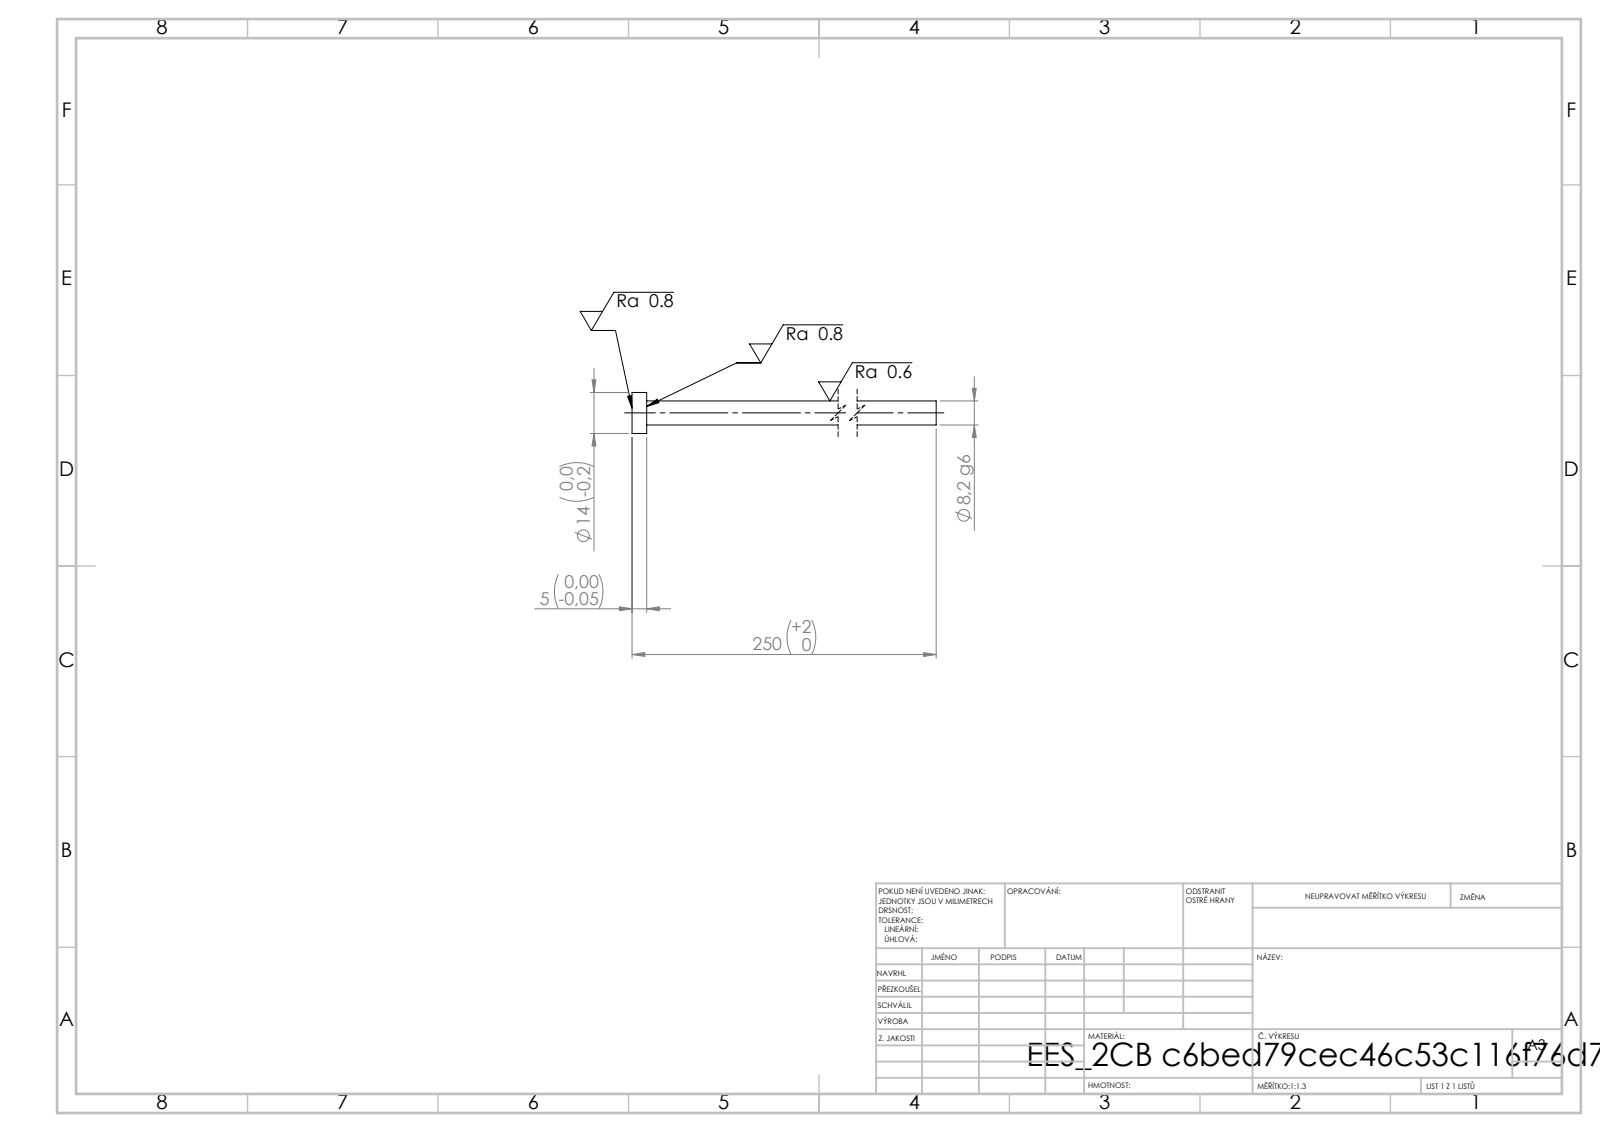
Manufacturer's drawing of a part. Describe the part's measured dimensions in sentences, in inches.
Its 3-D file was written by "SolidWorks 2019 (CONFIG_CONTROL_DESIGN)". It is 1 solid with 7 faces: 3 planar, 4 cylindrical and 0 other. Overall it measures 9.843 by 0.551 by 0.551 inches. Its volume is 0.837 cubic inches and its surface area 10.6 square inches. Round bosses or shafts: 1 of diameter 0.551, 1 of diameter 0.323. The main face-to-face distances are 0.197, 9.843, 9.646.
